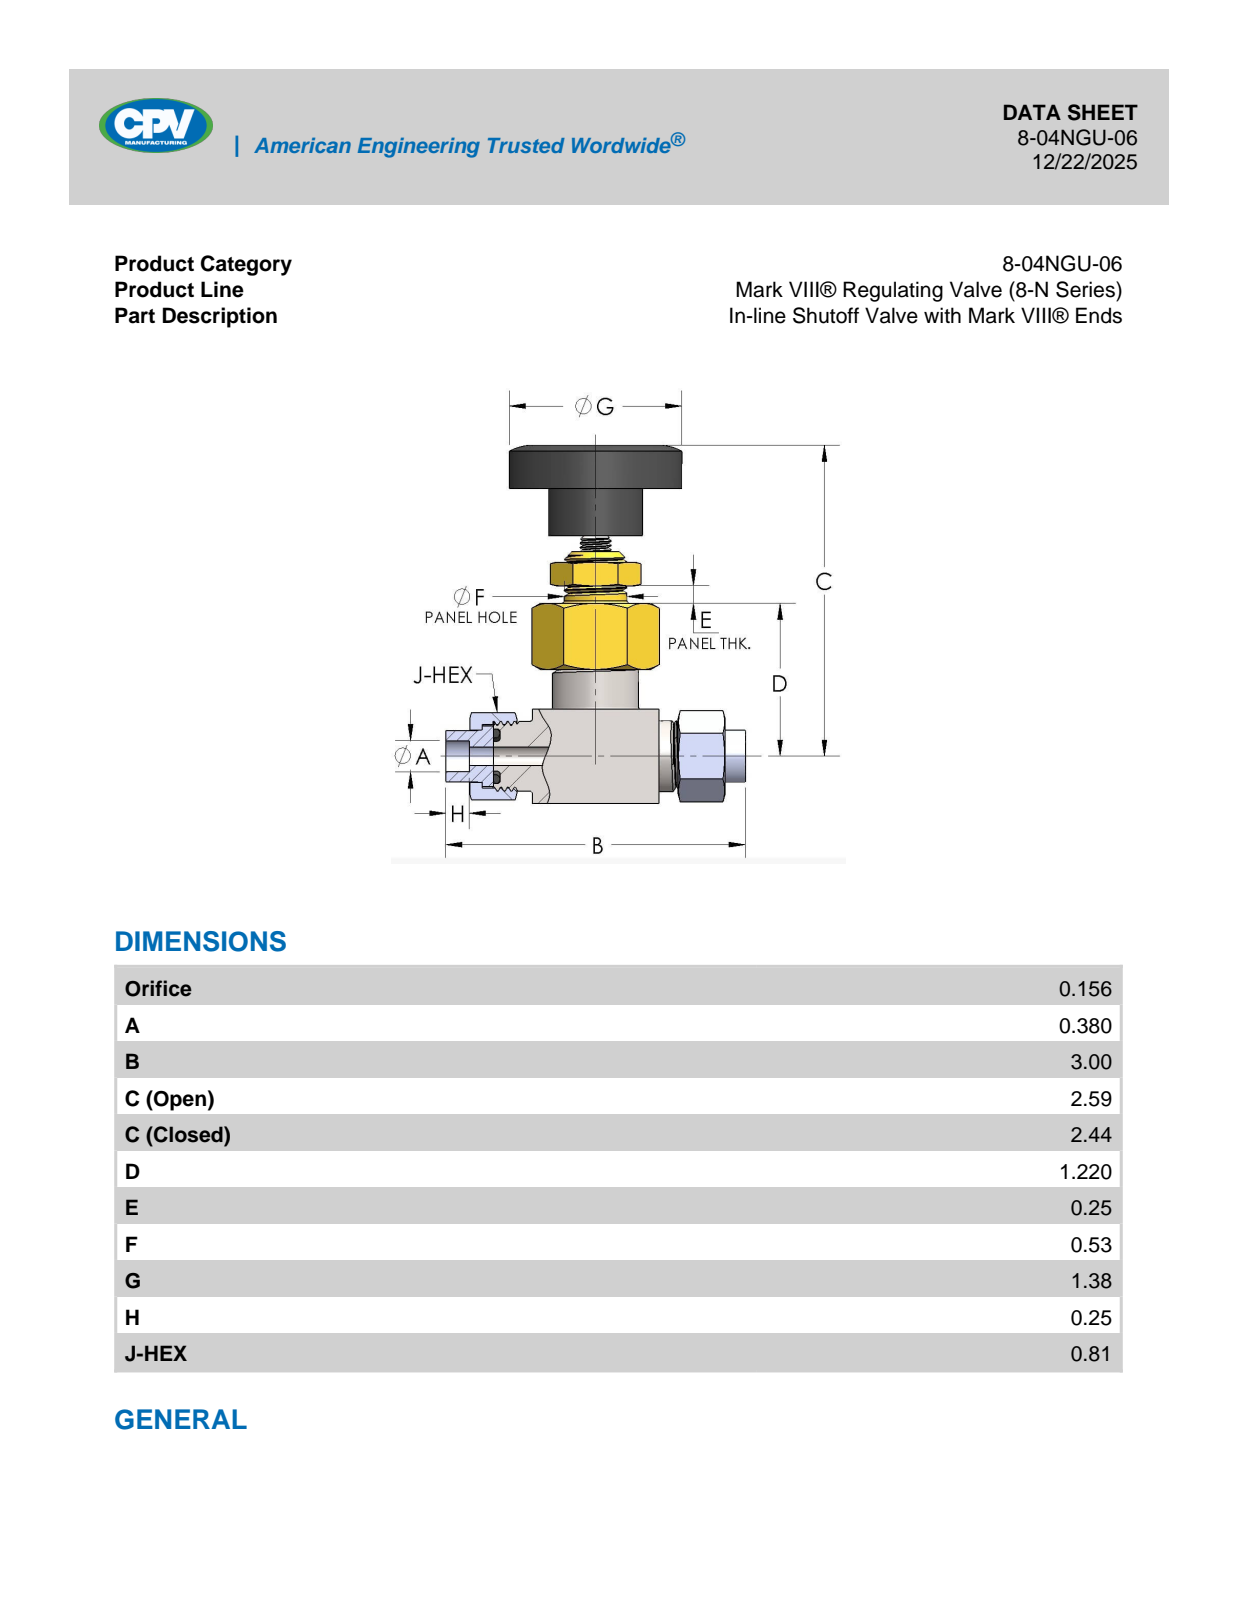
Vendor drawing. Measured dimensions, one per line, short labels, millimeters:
name: 8-04SGU-06
written by: SolidWorks 2018 (AUTOMOTIVE_DESIGN)
unit: mm
bodies: 2 solids, 184 faces (65 planar, 45 cylindrical, 74 other)
size: 75.4 × 63.8 × 35.1
volume: 38 760 mm³; area: 12 990 mm²
holes: 1× ⌀4.1, 1× ⌀4.9, 1× ⌀7.9, 1× ⌀9.7
bosses: 2× ⌀17.3, 1× ⌀35.1, 1× ⌀19.1, 1× ⌀13.5, 1× ⌀12.6, 1× ⌀6.4, 1× ⌀4.8
face distances: 8.8, 19.1, 19.8, 0.8, 22.4, 20.6, 64.2, 73, 20.6, 54.7
